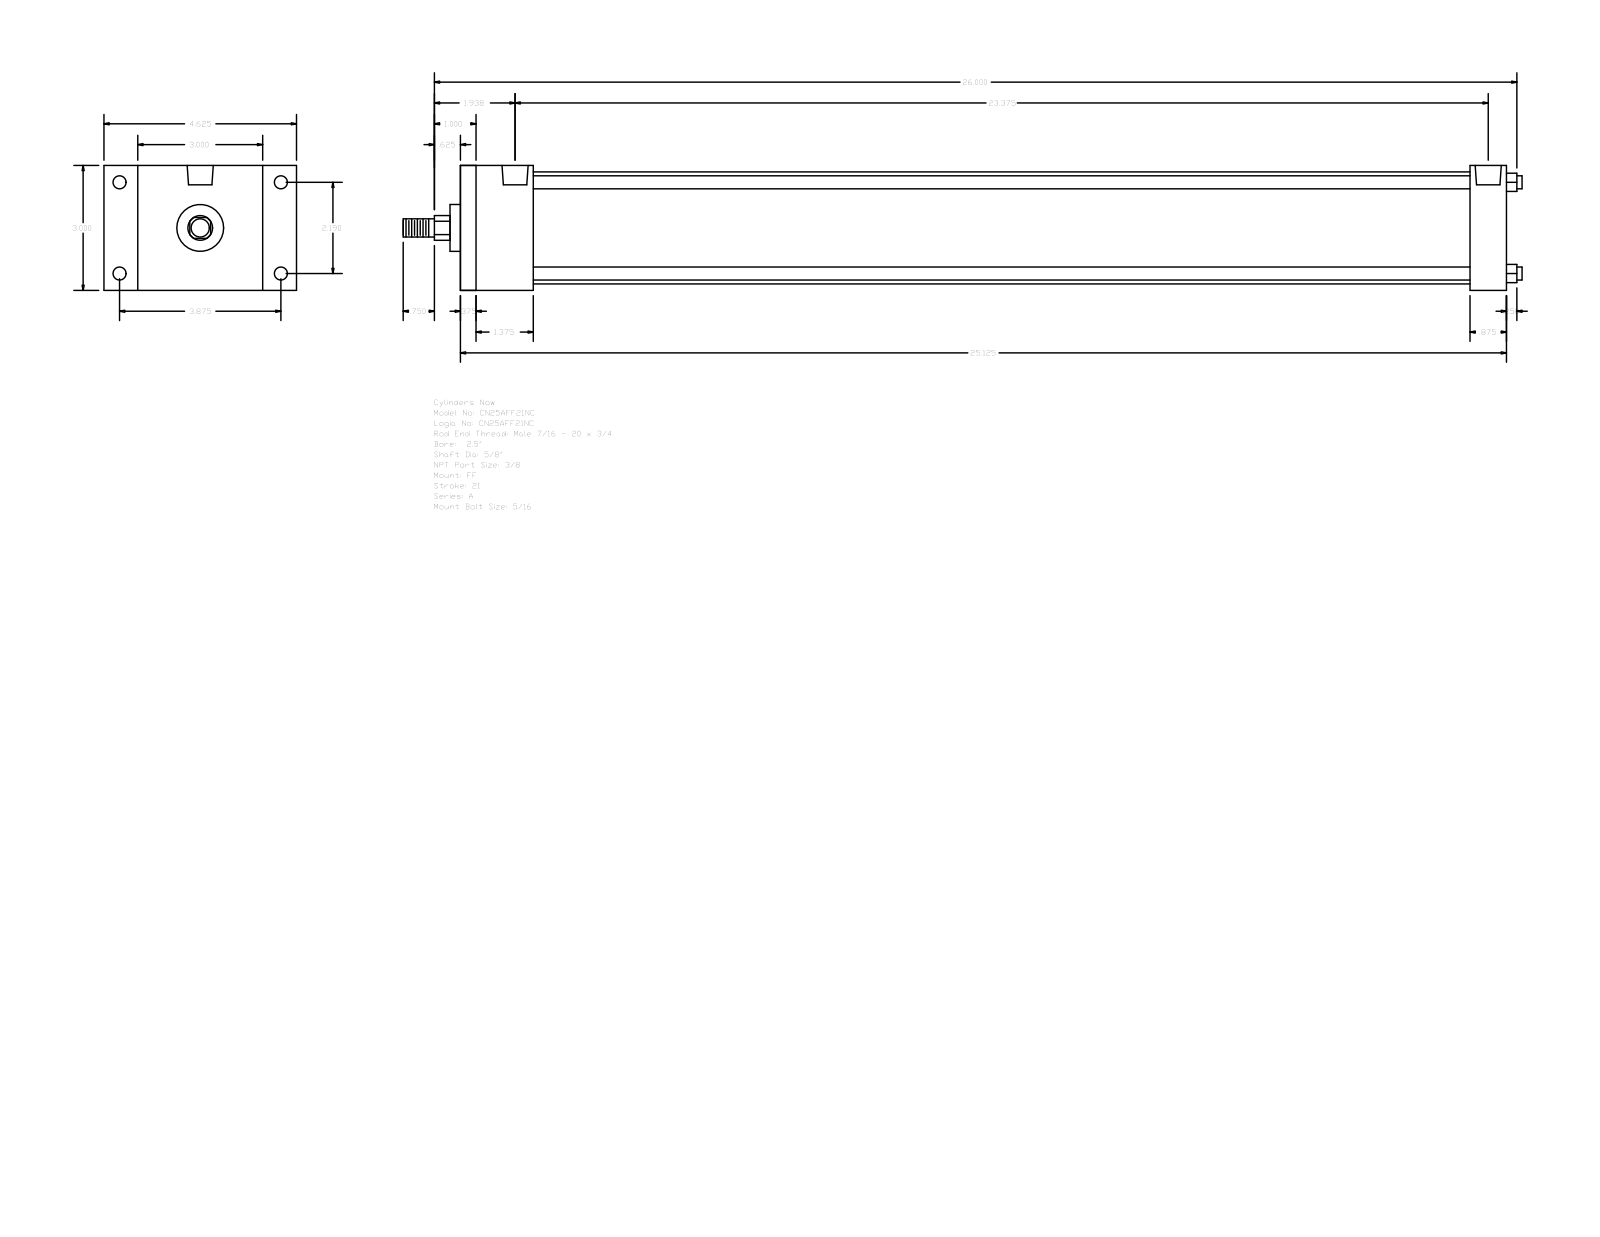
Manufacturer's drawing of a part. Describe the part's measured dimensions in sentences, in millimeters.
The part is named "A_FF__0250_0.625". Its 3-D file was written by "GSSL Pune (CONFIG_CONTROL_DESIGN)". It is 0 solids with 92 faces: 64 planar, 28 cylindrical and 0 other. Overall it measures 682.62 by 117.47 by 76.2 millimeters. Round holes: 4 of diameter 5.56, 4 of diameter 7.94, 2 of diameter 15.93. Round bosses or shafts: 4 of diameter 7.94, 1 of diameter 68.33, 1 of diameter 28.57, 1 of diameter 15.88, 1 of diameter 11.11. Partial cylindrical surfaces (rounded edges, fillets, slot ends): 1 of radius 7.54. The main face-to-face distances are 76.2, 638.17, 9.52, 628.65, 44.45, 34.93, 615.95, 606.43, 571.5, 593.72. The hole center spacings are 2.38, 55.62, 98.42, 113.05, 596.11, 598.49, 593.73.
